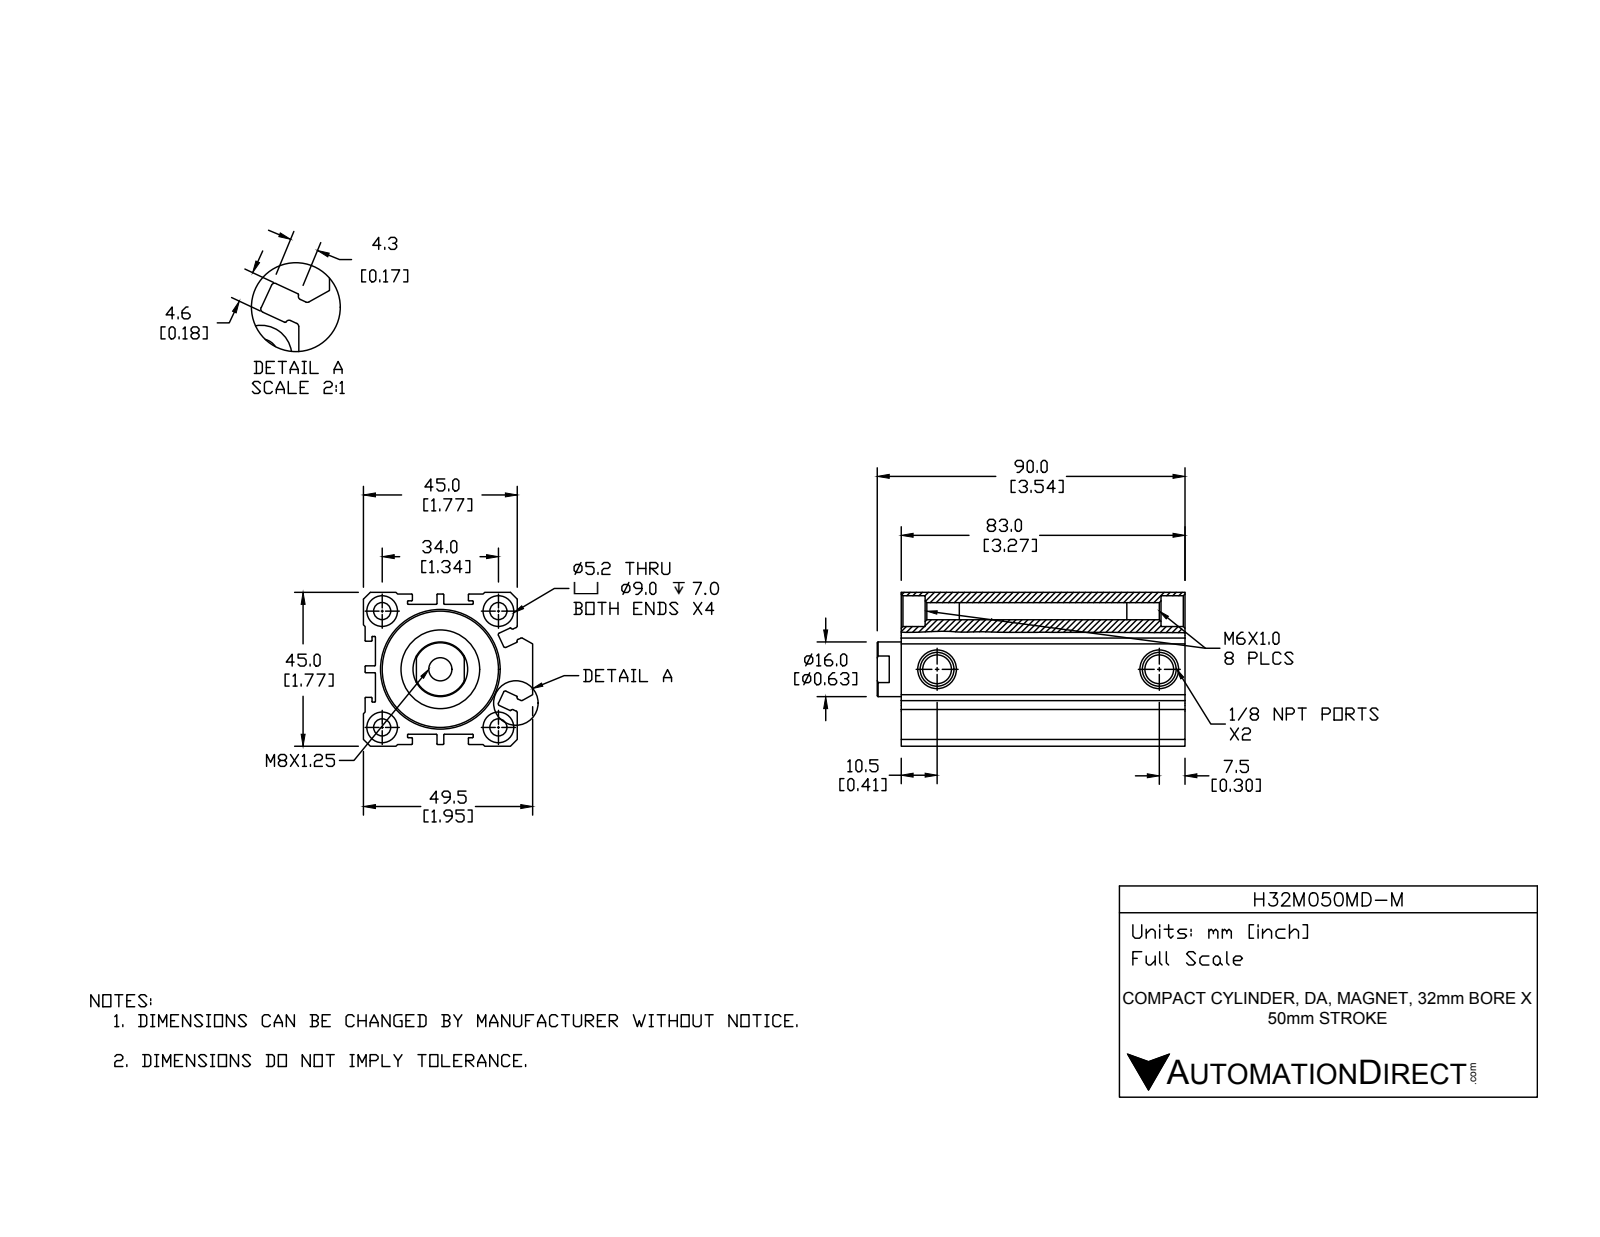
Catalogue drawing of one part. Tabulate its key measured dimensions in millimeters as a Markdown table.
| quantity | value |
| --- | --- |
| part name | H32M050MD-M-BODY; H32M050MD-M; H32M050MD-M-PISTON |
| STEP written by | SolidWorks 2015 (CONFIG_CONTROL_DESIGN) |
| units | millimeters |
| bodies | 2 solids, 255 faces (99 planar, 103 cylindrical, 53 other) |
| overall size | 90 × 49.5 × 45 |
| volume | 112 435 mm³ |
| surface area | 47 534 mm² |
| round holes (diameter × count) | 5 × 4, 9 × 4, 8.43 × 2, 6.8 × 1, 16 × 1, 23 × 1, 28 × 1, 32 × 1, 34 × 1 |
| round bosses / shafts (diameter × count) | 20 × 1 |
| partial cylindrical surfaces (radius × count) | 0.2 × 40, 0.5 × 12 |
| main face-to-face distances | 3.5, 41.5, 3, 45, 0.5, 44.5, 4.5, 41, 38, 21 |
| hole center spacings | 24.04, 34, 48.08, 65 |
